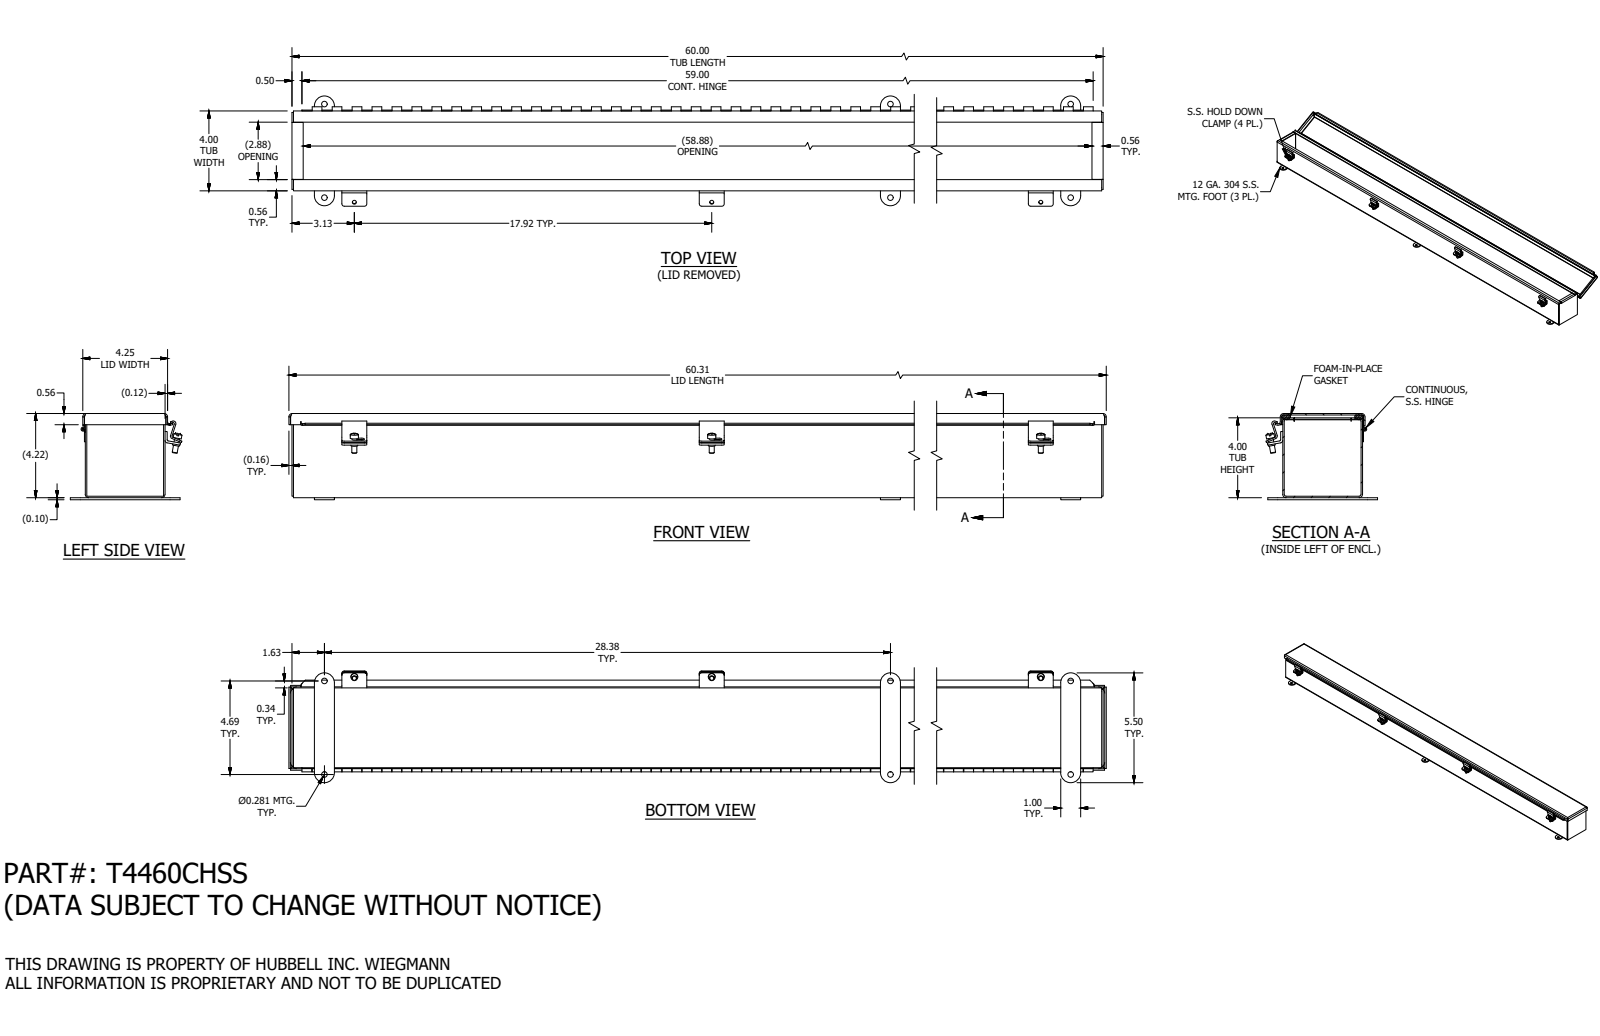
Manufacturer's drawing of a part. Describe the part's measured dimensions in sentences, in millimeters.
The part is named "T4460CHSS". Its 3-D file was written by "SolidWorks 2019 (AUTOMOTIVE_DESIGN)". It is 23 solids with 1024 faces: 613 planar, 365 cylindrical and 46 other. Overall it measures 1532 by 142.2 by 109.8 millimeters. Its volume is 1 652 000 cubic millimeters and its surface area 1 732 000 square millimeters. Round holes: 8 of diameter 2.8, 6 of diameter 7.1, 4 of diameter 5, 1 of diameter 2.9. Round bosses or shafts: 4 of diameter 10.4, 4 of diameter 8.7, 4 of diameter 6.4, 1 of diameter 5.1, 1 of diameter 2.5. Partial cylindrical surfaces (rounded edges, fillets, slot ends): 16 of radius 3.2, 11 of radius 2.4, 11 of radius 4.3, 8 of radius 2.2, 8 of radius 3.4, 6 of radius 12.7, 4 of radius 6.1, 3 of radius 1.6. The main face-to-face distances are 1.9, 99.7, 105.3, 101.6, 97.8, 107.1, 103.4, 5.5, 102.9, 3.2. The hole center spacings are 455.1, 19.1, 720.7, 730.5, 910.2, 119, 436, 455.1.
